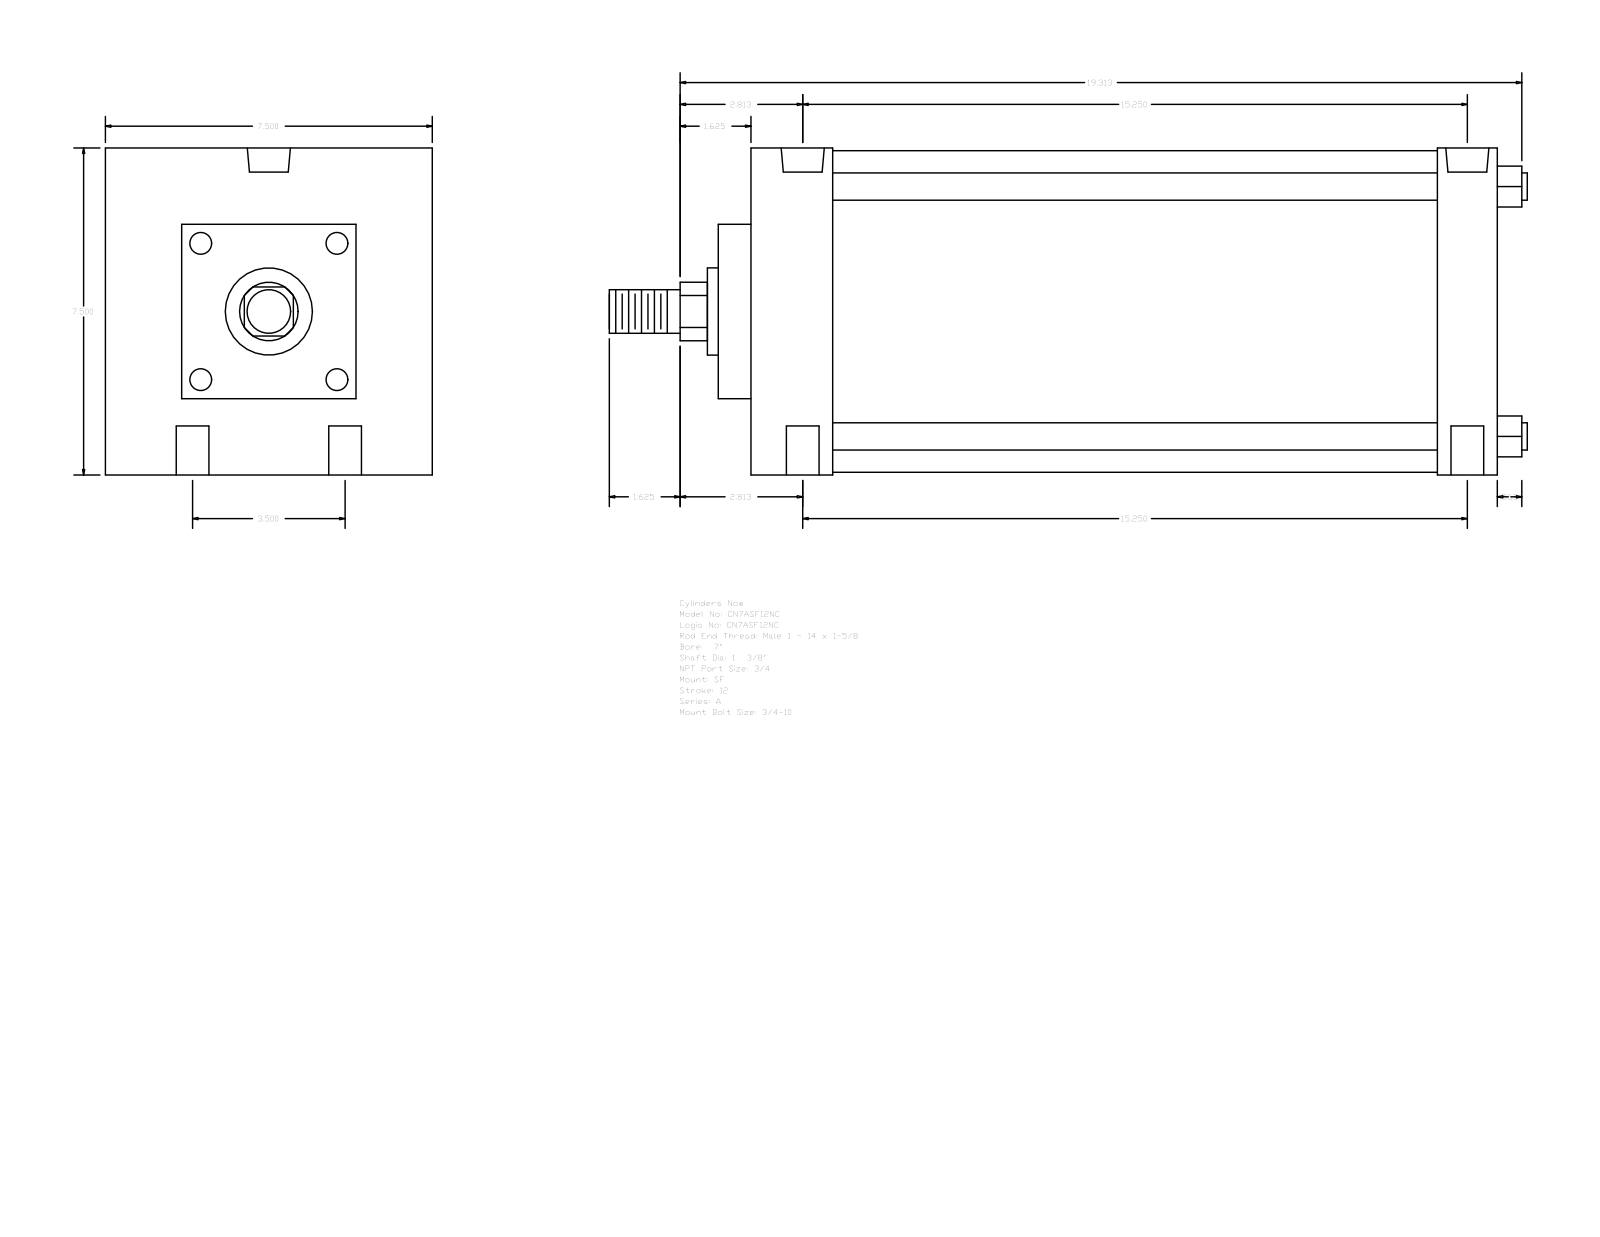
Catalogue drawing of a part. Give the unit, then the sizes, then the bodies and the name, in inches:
Units: inches
Overall size (bounding box): 21.063 × 7.5 × 7.5
Round holes (diameter × count): ⌀0.75 ×4, ⌀0.594 ×2, ⌀0.989 ×2
Round bosses / shafts (diameter × count): ⌀0.625 ×4, ⌀7.375 ×1, ⌀2 ×1, ⌀1.375 ×1, ⌀1 ×1
Partial cylindrical surfaces — rounded edges, fillets, slot ends (radius × count): R0.672 ×1
Main face-to-face distances: 7.5, 17.125, 0.75, 17.875, 2.625, 16.5, 1.875, 15.75, 13.875, 15.25
Hole centre spacings: 1.75, 15.35, 15.25, 3.5, 15.646, 14.812
Bodies: 0 solids, 93 faces (67 planar, 26 cylindrical, 0 other)
Part name (STEP PRODUCT): A_SF__0700_1.375
STEP written by: GSSL Pune (CONFIG_CONTROL_DESIGN)
